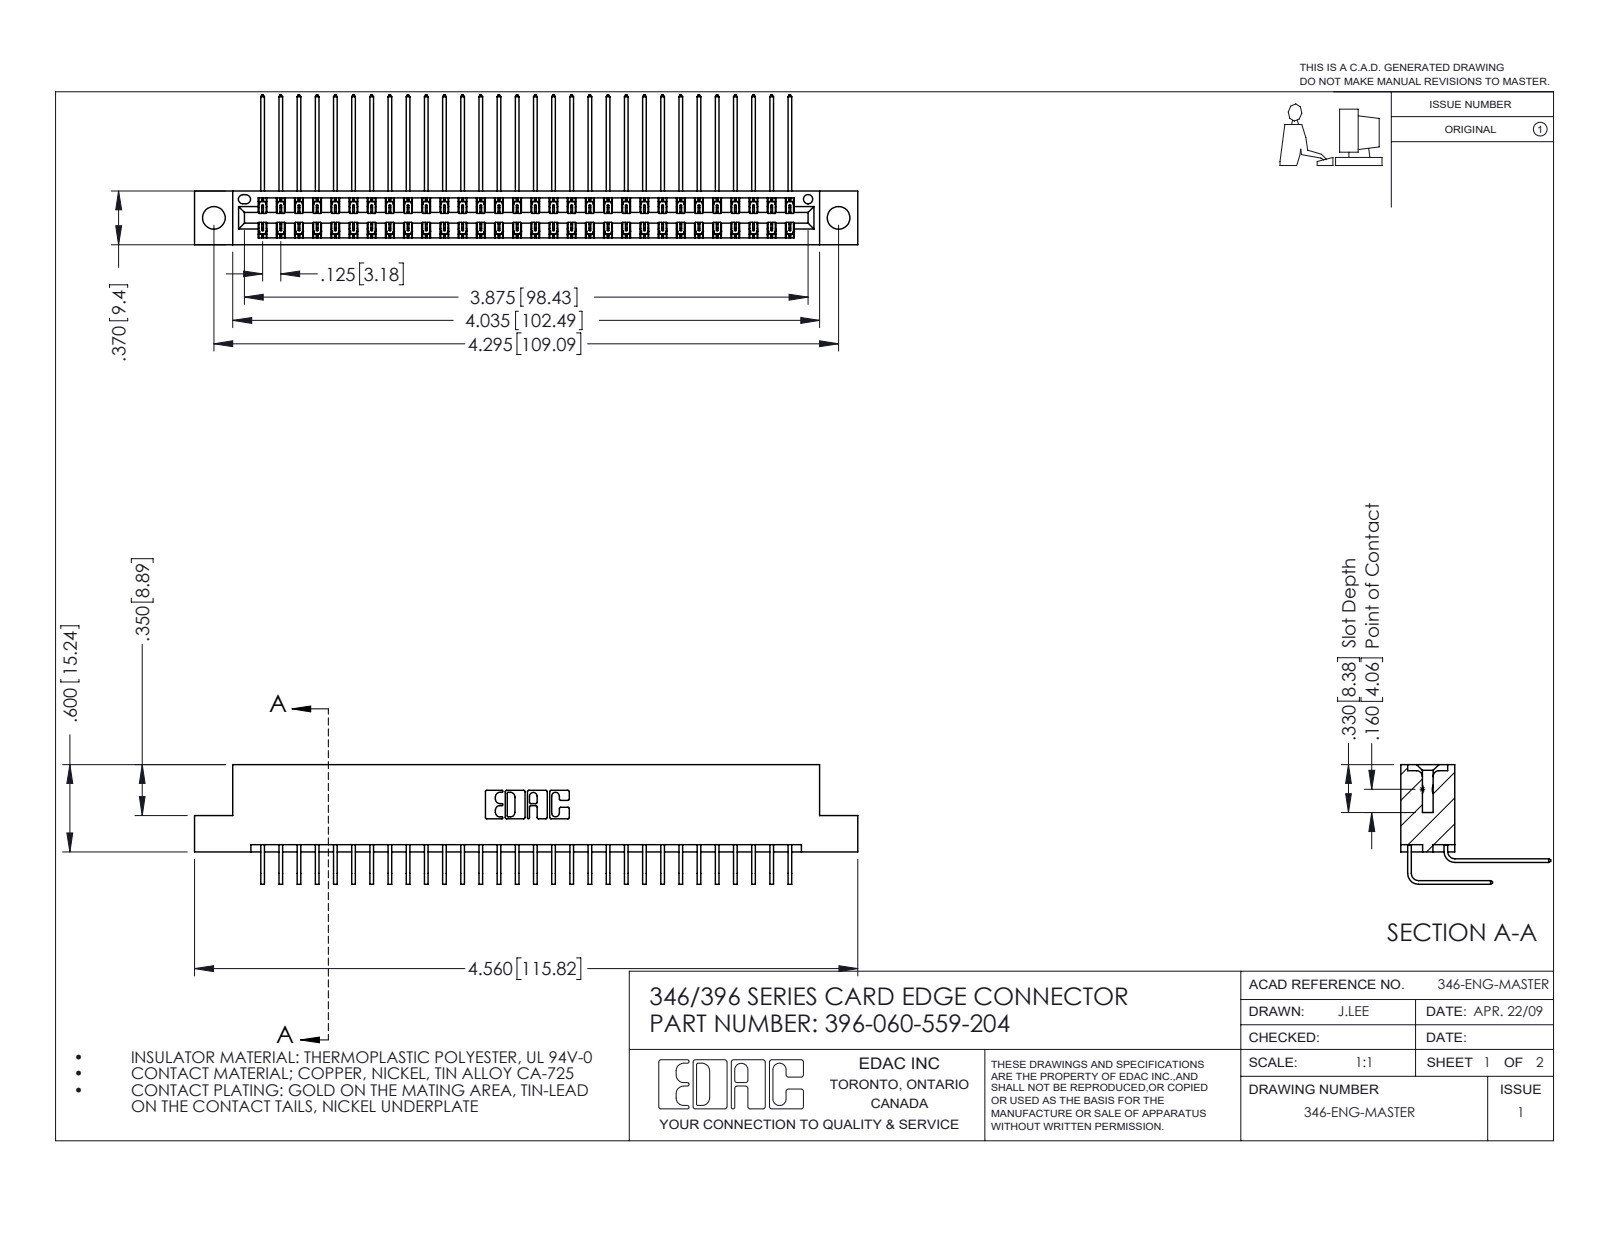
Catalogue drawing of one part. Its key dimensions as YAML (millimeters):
part_name: "345-292-001_559 Tail - 2; 345-292-001_558 559 Tail - 1; 396-060-559-204; 346 Part_Flush Mounting Lugs - 0.156 Dia-TH"
step_written_by: "SolidWorks 2016 (CONFIG_CONTROL_DESIGN)"
units: millimeters
bodies: {solids: 61, faces: 3362, planar: 2296, cylindrical: 1066, other: 0}
overall_size: [115.8, 26.2, 20.9]
volume: 11500
surface_area: 17040
round_holes:
  - {diameter: 4, count: 2}
  - {diameter: 1.6, count: 1}
partial_cylinders:
  - {radius: 0.2, count: 90}
  - {radius: 0.3, count: 22}
  - {radius: 0.2, count: 6}
  - {radius: 0.8, count: 6}
  - {radius: 0.7, count: 3}
  - {radius: 0.4, count: 2}
  - {radius: 0.6, count: 2}
  - {radius: 0.6, count: 2}
face_to_face_distances: [1.2, 8.2, 0.6, 6.4, 9.4, 1.8, 7.6, 7, 3.8, 5.6]
hole_center_spacings: [6.2, 103.8, 109.1]
